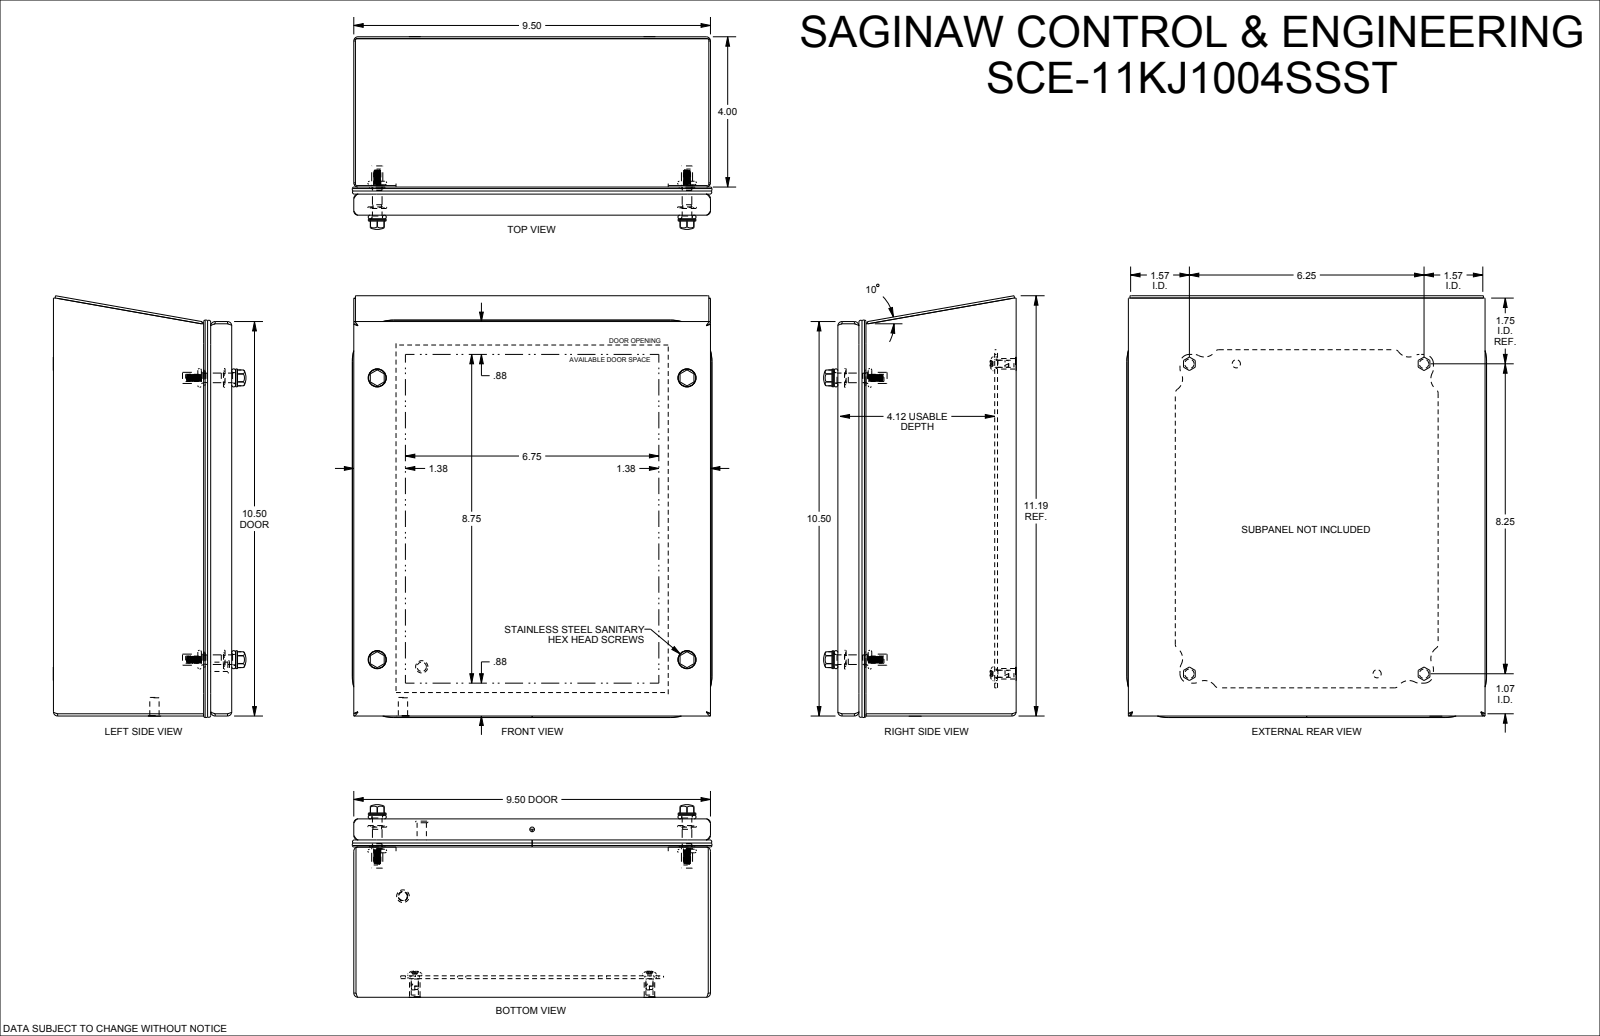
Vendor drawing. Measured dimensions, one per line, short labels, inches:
name: SCE-11KJ1004SSST
written by: SolidWorks 2021 (AUTOMOTIVE_DESIGN)
unit: in
bodies: 31 solids, 991 faces (349 planar, 309 cylindrical, 333 other)
size: 11.209 × 9.581 × 5.133
volume: 40.12 in³; area: 1 179 in²
holes: 8× ⌀0.19, 8× ⌀0.28, 4× ⌀0.25, 4× ⌀0.27, 4× ⌀0.32, 4× ⌀0.367, 2× ⌀0.218
bosses: 4× ⌀0.5, 4× ⌀0.475, 4× ⌀0.373, 4× ⌀0.296, 4× ⌀0.28, 4× ⌀0.256, 4× ⌀0.23, 4× ⌀0.189
rounds: 26× R0.05, 26× R0.11, 20× R0.02, 12× R0.125, 12× R0.25, 8× R0.344, 4× R0.005, 4× R0.012
face distances: 0.06, 4.688, 4.628, 4.748, 9.44, 4.192, 4.252, 0.571, 0.511, 4.117
hole spacings: 7.5, 7.938, 7.26, 8.25, 7.255, 8.245, 10.704, 10.704
